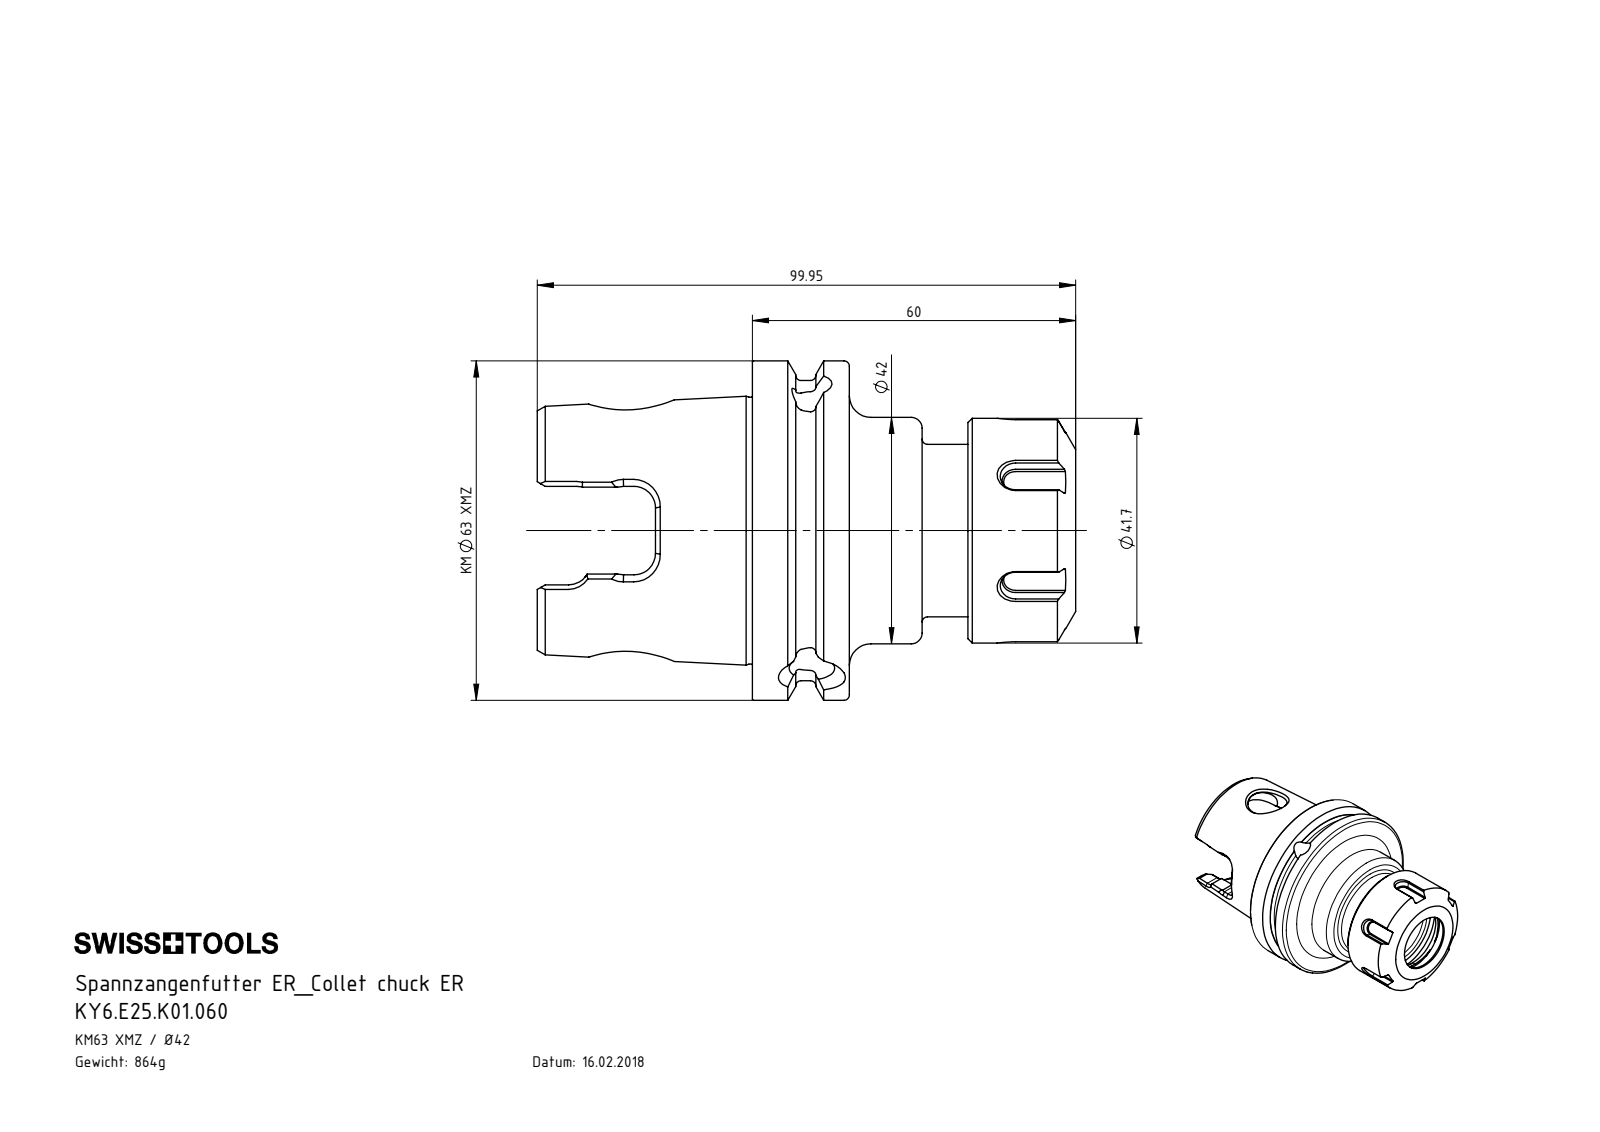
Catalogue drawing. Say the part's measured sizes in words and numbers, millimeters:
The part is named "KY6.E25.K01.060; E25-ER1.001.020; KY6-E25.K01.060_B". Its 3-D file was written by "SolidWorks 2017 (CONFIG_CONTROL_DESIGN)". It is 2 solids with 316 faces: 96 planar, 67 cylindrical and 153 other. Overall it measures 99.95 by 62.95 by 62.95 millimeters. Its volume is 110 118 cubic millimeters and its surface area 31 271 square millimeters. Round holes: 2 of diameter 7.47, 1 of diameter 8, 1 of diameter 8.48, 1 of diameter 10, 1 of diameter 11.5, 1 of diameter 14.5, 1 of diameter 18, 1 of diameter 20.9, 1 of diameter 30.5, 1 of diameter 31.1, 1 of diameter 32.5, 1 of diameter 35.27. Round bosses or shafts: 1 of diameter 62.95, 1 of diameter 55.7, 1 of diameter 42, 1 of diameter 41.7, 1 of diameter 32. Partial cylindrical surfaces (rounded edges, fillets, slot ends): 6 of radius 4, 2 of radius 7.04, 2 of radius 12.17. The main face-to-face distances are 18, 1.1, 19.1, 41.1, 40, 22, 61.1, 60, 42, 20.
